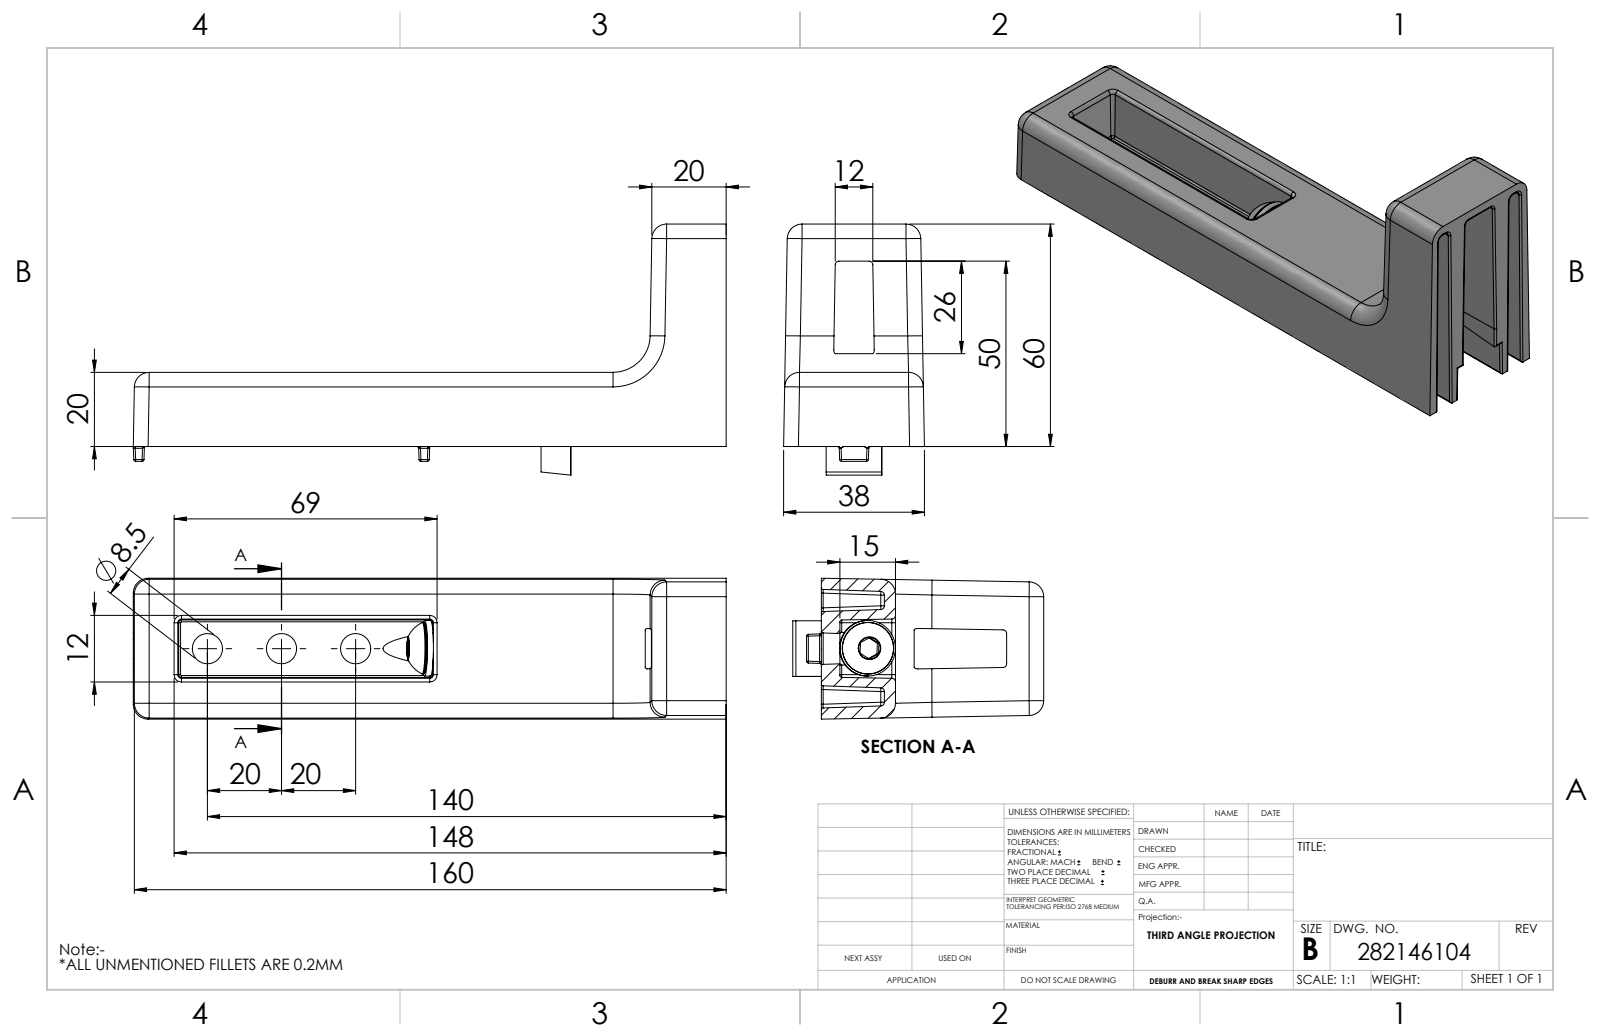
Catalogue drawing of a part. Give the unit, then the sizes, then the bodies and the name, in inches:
Units: inches
Overall size (bounding box): 6.3 × 2.666 × 1.496
Round holes (diameter × count): ⌀0.268 ×1, ⌀0.331 ×1
Round bosses / shafts (diameter × count): ⌀0.591 ×1, ⌀0.315 ×1
Partial cylindrical surfaces — rounded edges, fillets, slot ends (radius × count): R0.02 ×81, R0.039 ×66, R0.157 ×10, R0.059 ×4, R0.315 ×1, R0.394 ×1
Main face-to-face distances: 0.787, 0.423, 1.022, 0.039, 0.626, 1.05, 1.063, 1.062, 0.591, 0.118
Volume: 4.814 in³ · Surface area: 70.17 in²
Bodies: 4 solids, 480 faces (107 planar, 208 cylindrical, 165 other)
Part name (STEP PRODUCT): 282146104
STEP written by: SolidWorks 2014 (AUTOMOTIVE_DESIGN)
